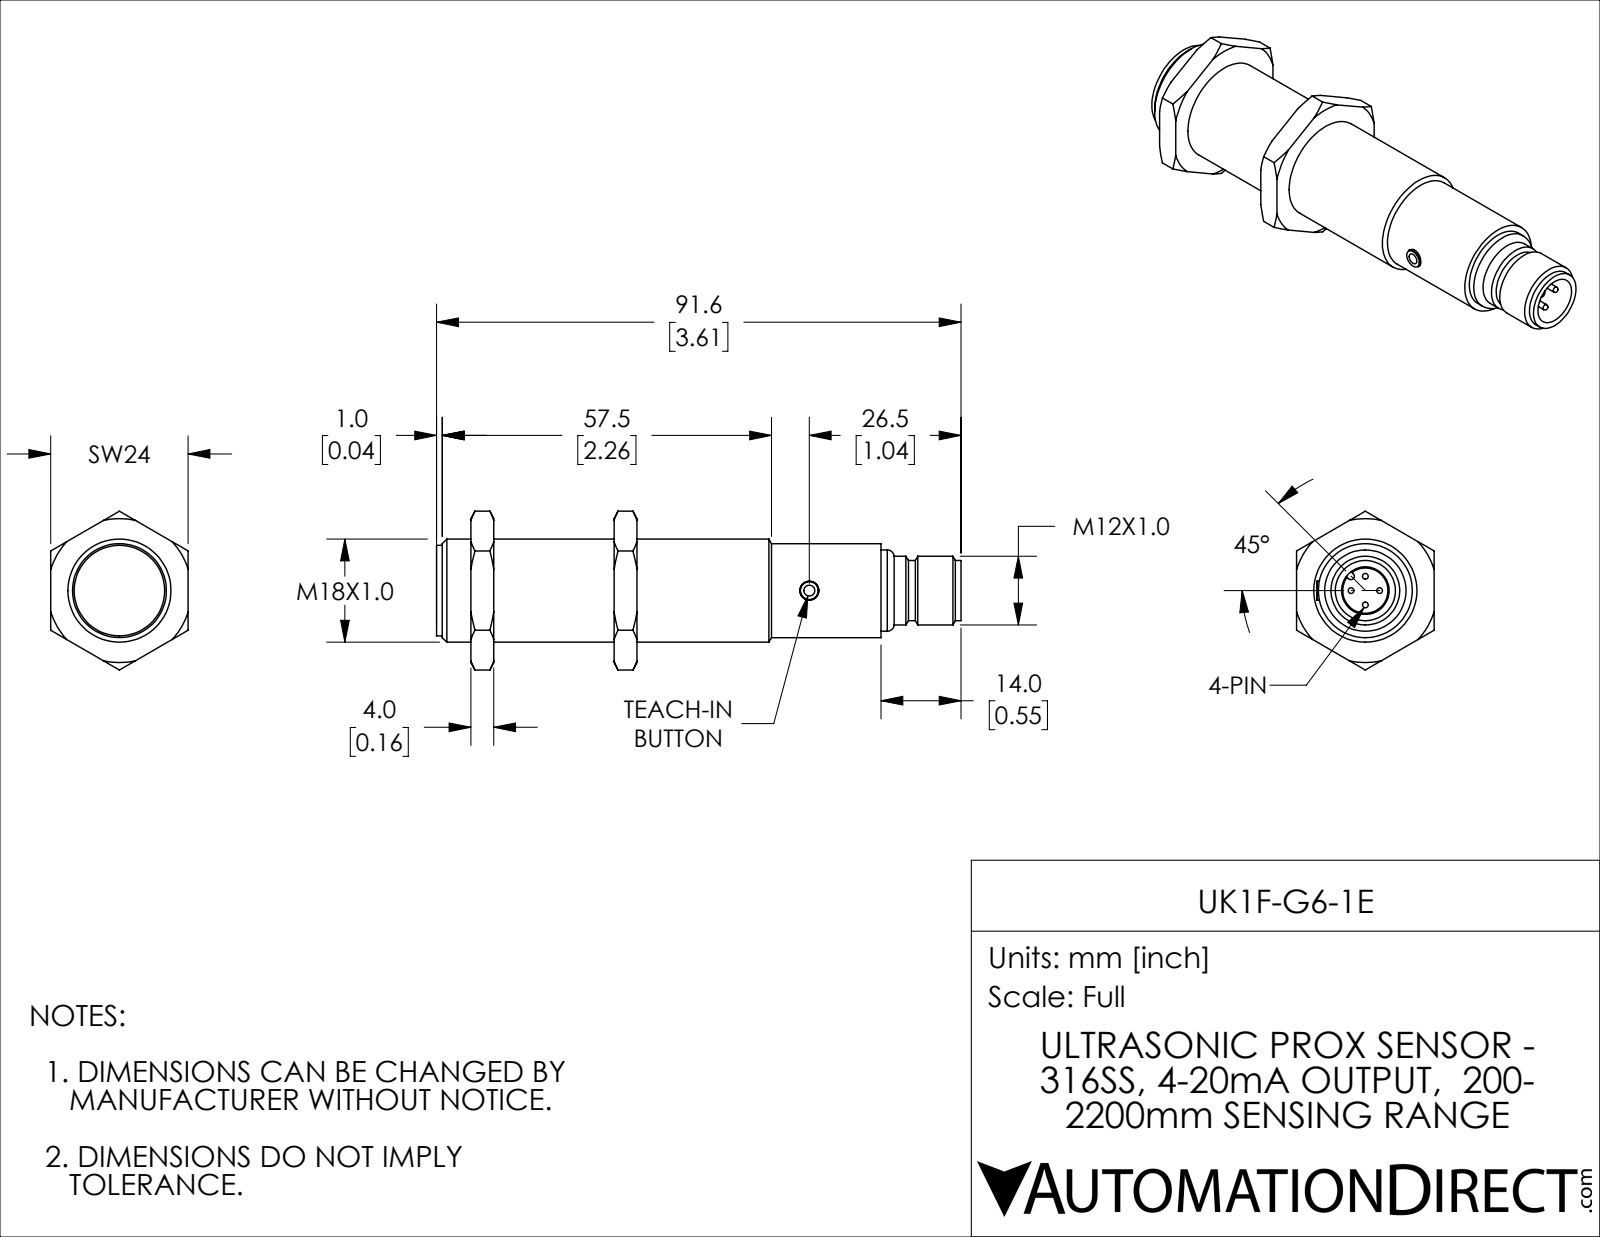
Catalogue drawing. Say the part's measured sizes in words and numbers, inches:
The part is named "UK1F-G6-1E". Its 3-D file was written by "SolidWorks 2018 (AUTOMOTIVE_DESIGN)". It is 4 solids with 113 faces: 27 planar, 35 cylindrical and 51 other. Overall it measures 3.606 by 1.091 by 0.945 inches. Its volume is 1.338 cubic inches and its surface area 11.97 square inches. Round holes: 1 of diameter 0.13, 1 of diameter 0.327, 1 of diameter 0.709. Round bosses or shafts: 4 of diameter 0.039, 1 of diameter 0.646, 1 of diameter 0.622, 1 of diameter 0.559, 1 of diameter 0.472, 1 of diameter 0.413. Partial cylindrical surfaces (rounded edges, fillets, slot ends): 1 of radius 0.024. The main face-to-face distances are 0.984, 0.157, 0.945, 1.142, 0.827, 0.236, 0.394, 1.22, 1.378, 3.055.
